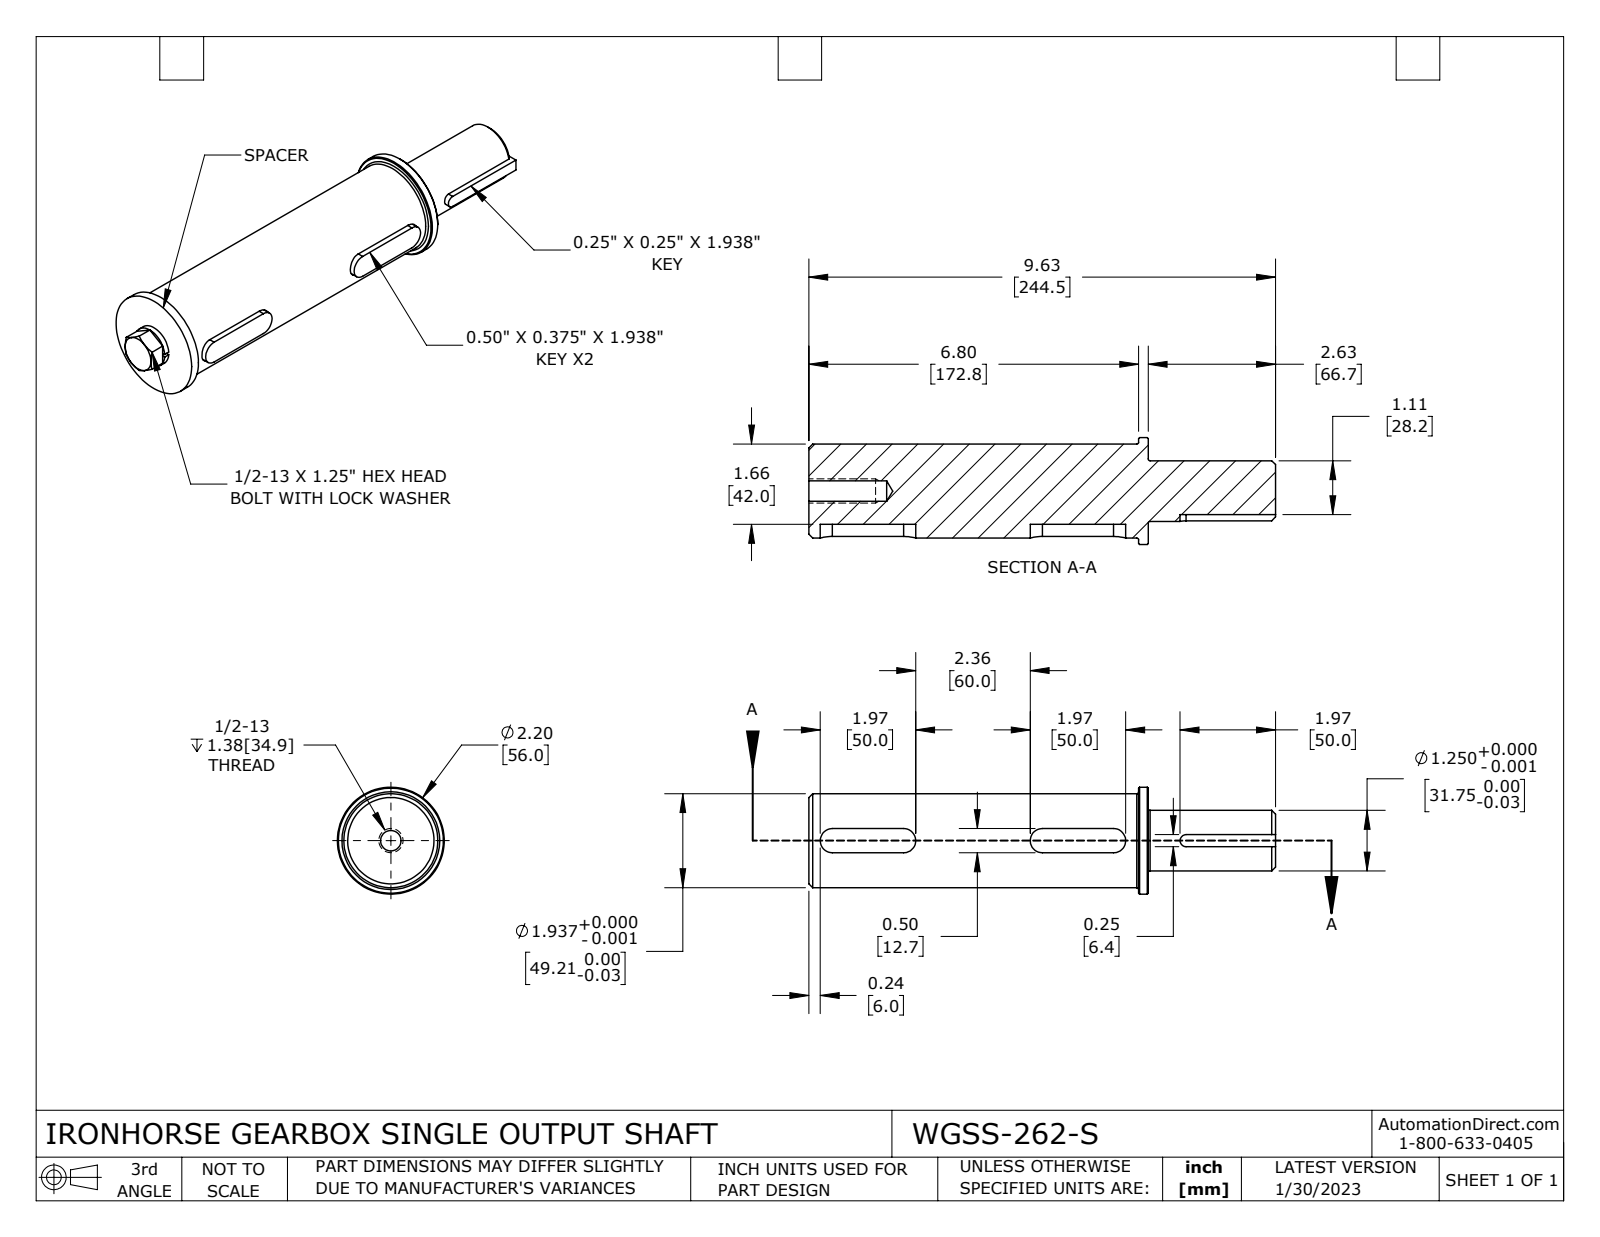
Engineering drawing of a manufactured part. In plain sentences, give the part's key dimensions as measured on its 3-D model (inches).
The part is named "WGSS-262-S". Its 3-D file was written by "SolidWorks 2021 (CONFIG_CONTROL_DESIGN)". It is 7 solids with 93 faces: 41 planar, 31 cylindrical and 21 other. Overall it measures 10.285 by 2.205 by 2.205 inches. Its volume is 25.16 cubic inches and its surface area 87.76 square inches. Round holes: 1 of diameter 0.422, 1 of diameter 0.512, 1 of diameter 0.557. Round bosses or shafts: 1 of diameter 2.205, 1 of diameter 1.937, 1 of diameter 1.25, 1 of diameter 0.869, 1 of diameter 0.5. Partial cylindrical surfaces (rounded edges, fillets, slot ends): 8 of radius 0.25, 1 of radius 0.125. The main face-to-face distances are 0.197, 7, 7.197, 0.375, 0.5, 9.823, 9.626, 2.626, 0.199, 0.574.
